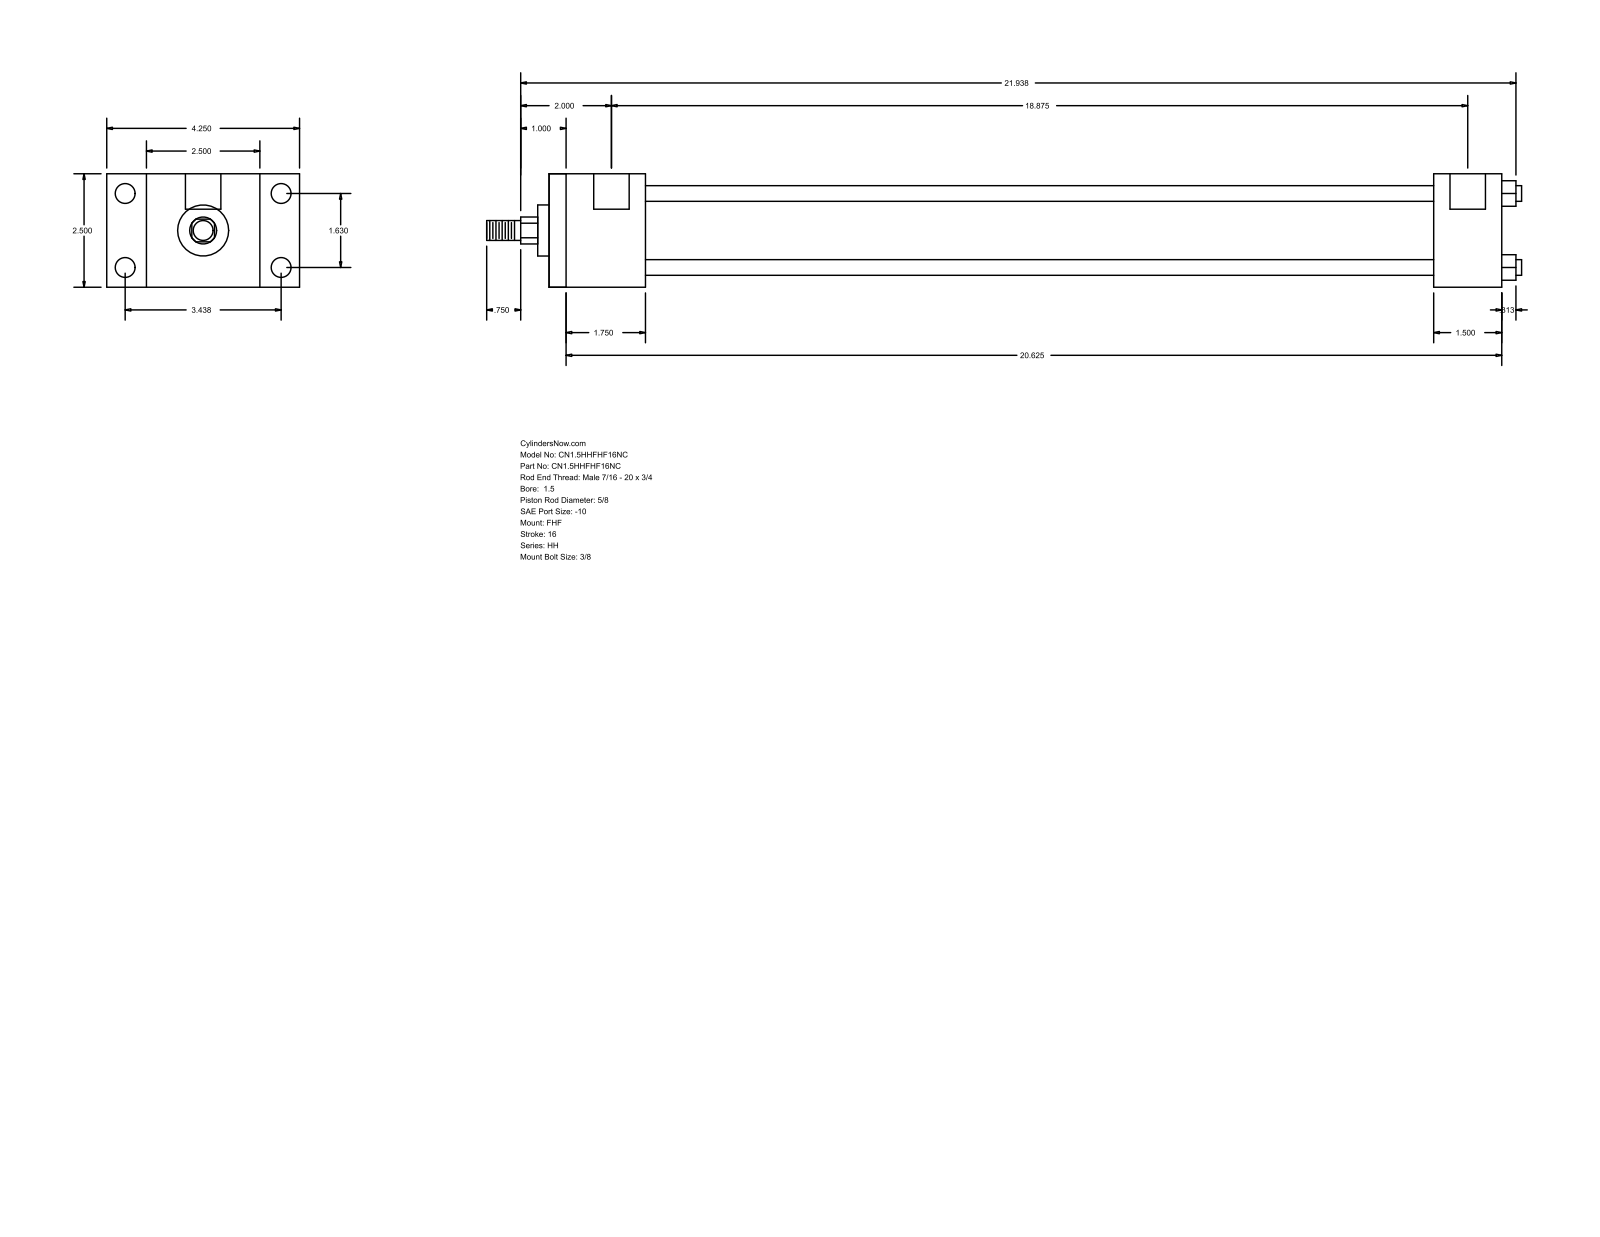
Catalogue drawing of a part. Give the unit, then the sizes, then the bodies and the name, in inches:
Units: inches
Overall size (bounding box): 22.813 × 4.25 × 2.5
Round holes (diameter × count): ⌀0.219 ×4, ⌀0.438 ×4, ⌀0.781 ×2
Round bosses / shafts (diameter × count): ⌀0.345 ×4, ⌀1.75 ×1, ⌀1.125 ×1, ⌀0.625 ×1, ⌀0.437 ×1
Partial cylindrical surfaces — rounded edges, fillets, slot ends (radius × count): R0.297 ×1
Main face-to-face distances: 2.5, 0.875, 3.375, 2.125, 4.25, 21, 18.875, 19.5, 17.375, 1.5
Hole centre spacings: 1.63, 3.438, 3.805, 19, 0.062, 0.063, 18.875, 18.937
Bodies: 0 solids, 88 faces (60 planar, 28 cylindrical, 0 other)
Part name (STEP PRODUCT): HH_FHF__0150_0.625
STEP written by: GSSL Pune (CONFIG_CONTROL_DESIGN)
